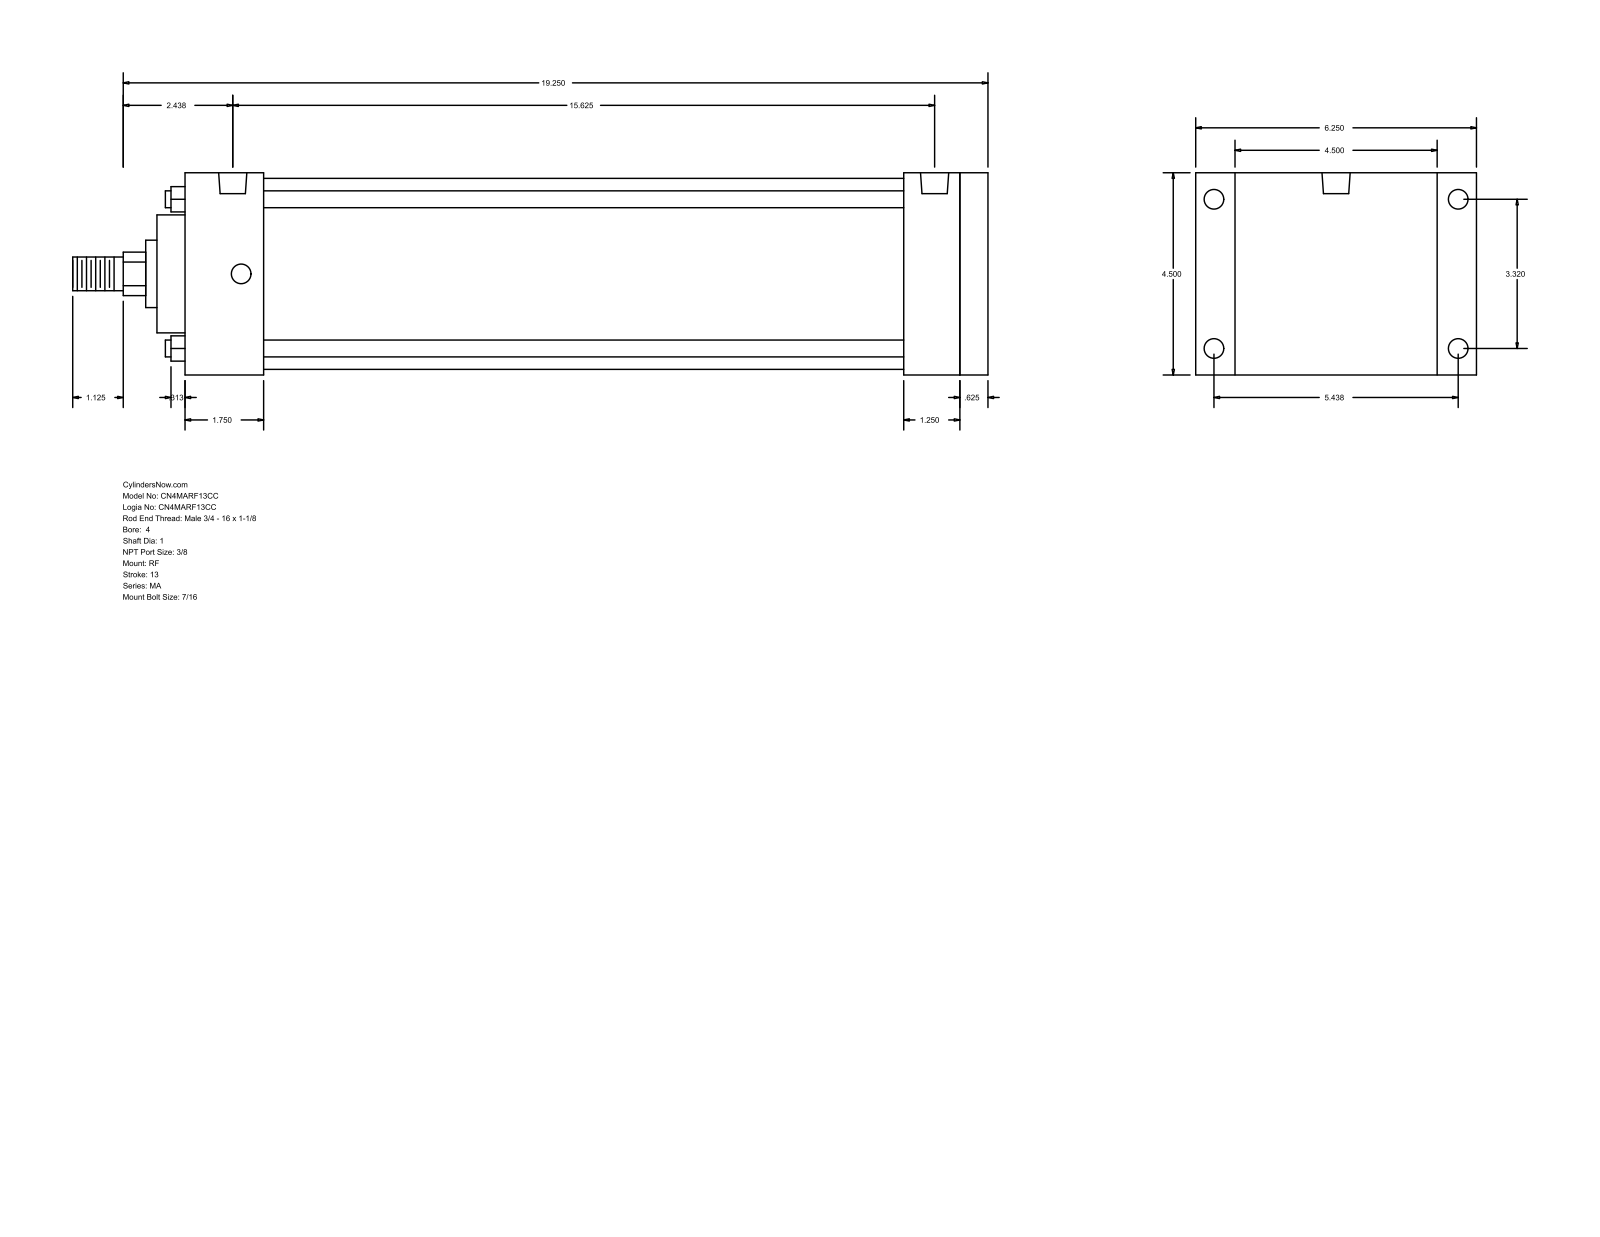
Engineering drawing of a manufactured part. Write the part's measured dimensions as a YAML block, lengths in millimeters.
part_name: "MA_RF__0400_1"
step_written_by: "GSSL Pune (CONFIG_CONTROL_DESIGN)"
units: millimeters
bodies: {solids: 0, faces: 94, planar: 65, cylindrical: 29, other: 0}
overall_size: [517.52, 158.75, 114.3]
round_holes:
  - {diameter: 11.11, count: 8}
  - {diameter: 15.93, count: 2}
round_bosses_or_shafts:
  - {diameter: 9.53, count: 4}
  - {diameter: 107.95, count: 1}
  - {diameter: 66.67, count: 1}
  - {diameter: 38.1, count: 1}
  - {diameter: 25.4, count: 1}
  - {diameter: 19.05, count: 1}
partial_cylinders:
  - {radius: 12.29, count: 1}
face_to_face_distances: [114.3, 454.03, 438.15, 15.88, 22.23, 136.53, 406.4, 31.75, 47.63, 44.46]
hole_center_spacings: [84.32, 138.12, 161.82, 387.35, 4.76, 4.77, 392.11, 392.12]
